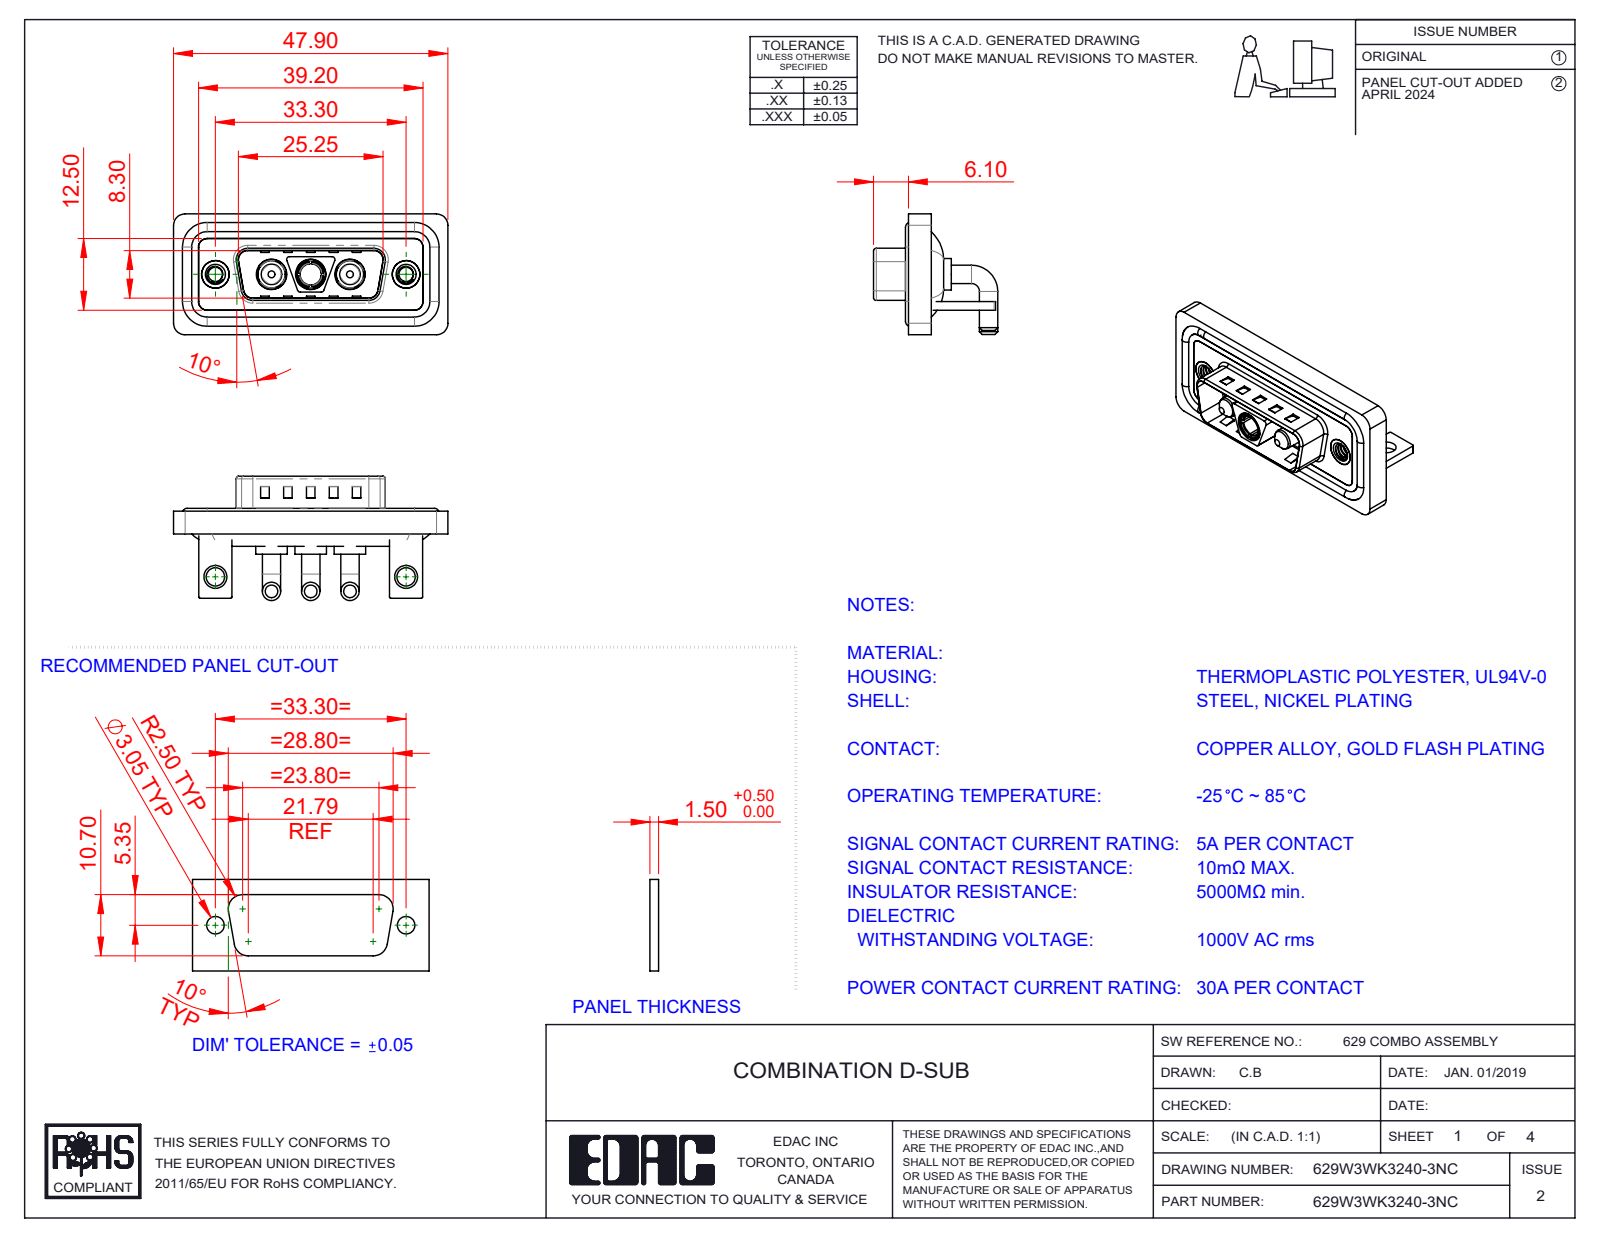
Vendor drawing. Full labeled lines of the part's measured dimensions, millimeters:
Part name (STEP PRODUCT): 629Combo Stabilizer Bracket; 629Combo Shell Rear_15 Contacts; 629Combo Housing_3WK3; Power Socket_30A RA (+5 more)
STEP written by: SolidWorks 2023 (CONFIG_CONTROL_DESIGN)
Units: millimetres
Bodies: 15 solids, 659 faces (251 planar, 274 cylindrical, 134 other)
Overall size (bounding box): 47.9 × 21.7 × 21.1
Volume: 6 242 mm³ · Surface area: 10 060 mm²
Round holes (diameter × count): ⌀4.85 ×3, ⌀5.3 ×3, ⌀2.5 ×2, ⌀3.2 ×2, ⌀4 ×2, ⌀4.8 ×2, ⌀5 ×2, ⌀3.7 ×1
Round bosses / shafts (diameter × count): ⌀3.2 ×6, ⌀1.6 ×4, ⌀5.5 ×3, ⌀5.2 ×3, ⌀4.75 ×3, ⌀3.75 ×3, ⌀4.9 ×2, ⌀3.6 ×2
Partial cylindrical surfaces — rounded edges, fillets, slot ends (radius × count): R2 ×21, R1.5 ×18, R0.25 ×16, R0.5 ×13, R1.6 ×8, R0.6 ×4, R0.65 ×4, R0.9 ×4
Main face-to-face distances: 0.4, 1.5, 0.8, 2.9, 1.1, 2.1, 3.7, 1.6, 1.2, 4.5
Hole centre spacings: 6.85, 9.8, 16.65, 23.5, 33.3, 13.7
